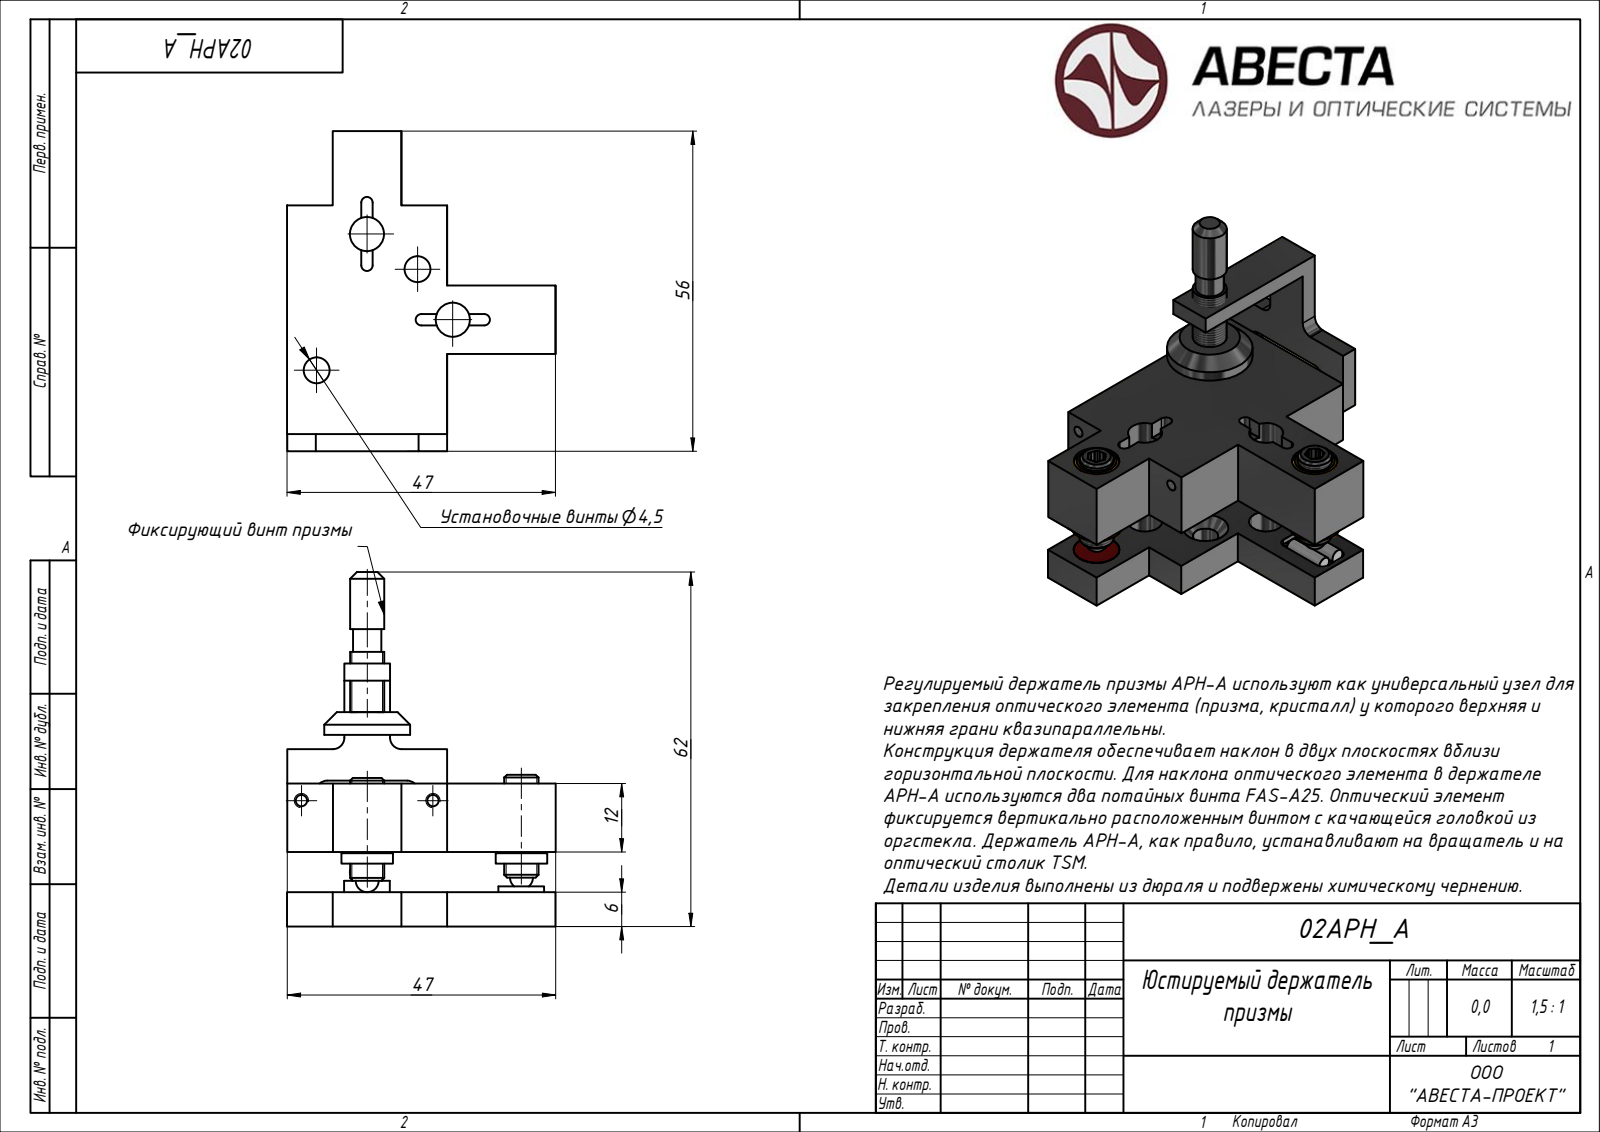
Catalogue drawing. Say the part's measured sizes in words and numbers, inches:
The part is named "Block 01; Block 02". Its 3-D file was written by "ST-DEVELOPER v15 (AUTOMOTIVE_DESIGN)". It is 9 solids with 343 faces: 0 planar, 0 cylindrical and 343 other. Overall it measures 2.442 by 2.323 by 1.86 inches. Its volume is 0.56 cubic inches and its surface area 22.18 square inches.
